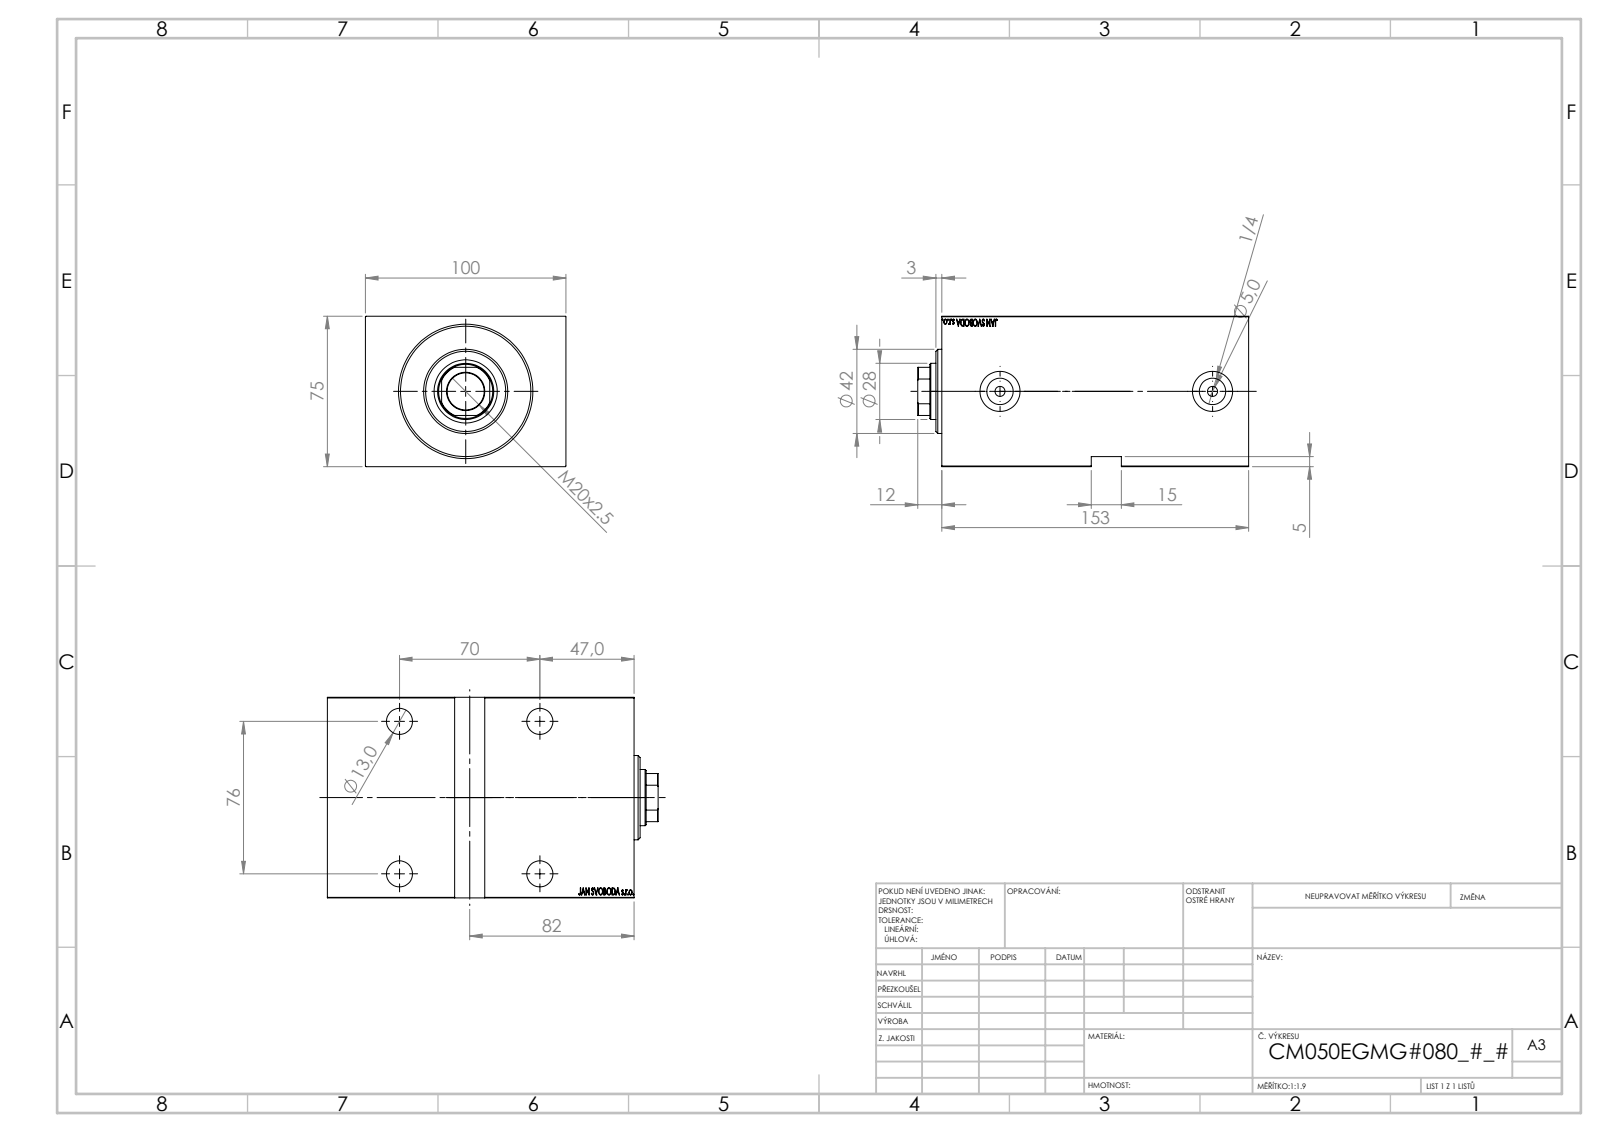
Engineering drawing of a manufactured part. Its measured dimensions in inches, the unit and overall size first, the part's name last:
Units: inches
Overall size (bounding box): 6.496 × 3.937 × 2.953
Round holes (diameter × count): ⌀0.512 ×4, ⌀0.748 ×4, ⌀0.197 ×2, ⌀0.518 ×2, ⌀0.787 ×2, ⌀0.728 ×1, ⌀1.102 ×1, ⌀1.24 ×1, ⌀1.969 ×1, ⌀2.047 ×1, ⌀2.559 ×1
Round bosses / shafts (diameter × count): ⌀1.654 ×1
Partial cylindrical surfaces — rounded edges, fillets, slot ends (radius × count): R0.531 ×1
Main face-to-face distances: 2.953, 3.937, 6.024, 0.551, 5.472, 0.197, 5.827, 5.276, 5.37, 4.819
Hole centre spacings: 2.756, 2.992, 4.068, 4.173
Volume: 58.43 in³ · Surface area: 212 in²
Bodies: 3 solids, 861 faces (413 planar, 54 cylindrical, 394 other)
Part name (STEP PRODUCT): V450CM_VC_B; V450CM_E_Body; V450CM_E_VCP
STEP written by: SolidWorks 2019 (CONFIG_CONTROL_DESIGN)
